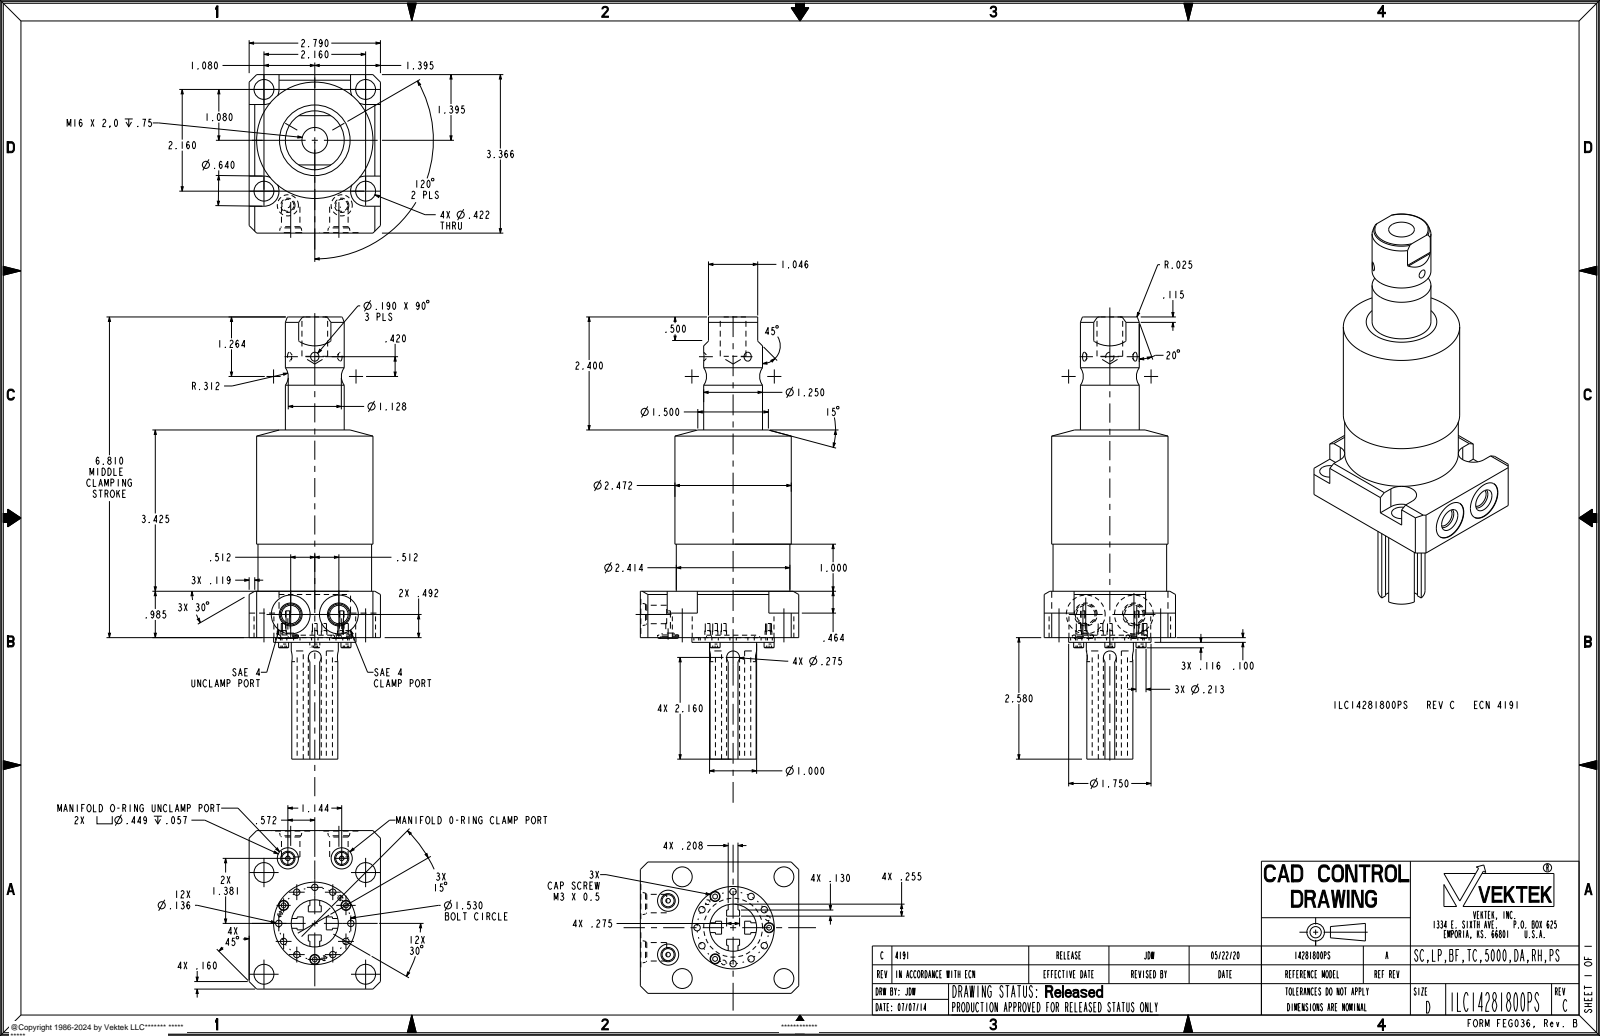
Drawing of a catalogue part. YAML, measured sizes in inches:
part_name: "ILC14281800PS"
step_written_by: "PRO/ENGINEER BY PARAMETRIC TECHNOLOGY CORPORATION, 2013320 (AUTOMOTIVE_DESIGN)"
units: inches
bodies: {solids: 1, faces: 283, planar: 133, cylindrical: 112, other: 38}
overall_size: [9.39, 3.366, 2.79]
volume: 28.24
surface_area: 88.39
round_holes:
  - {diameter: 0.136, count: 12}
  - {diameter: 0.1, count: 6}
  - {diameter: 0.422, count: 4}
  - {diameter: 0.098, count: 2}
  - {diameter: 0.256, count: 2}
  - {diameter: 0.392, count: 2}
  - {diameter: 0.449, count: 2}
  - {diameter: 0.825, count: 2}
  - {diameter: 0.546, count: 1}
  - {diameter: 1.13, count: 1}
round_bosses_or_shafts:
  - {diameter: 0.118, count: 6}
  - {diameter: 0.213, count: 3}
  - {diameter: 2.472, count: 1}
  - {diameter: 2.414, count: 1}
  - {diameter: 1.75, count: 1}
  - {diameter: 1.25, count: 1}
  - {diameter: 1, count: 1}
  - {diameter: 0.917, count: 1}
partial_cylinders:
  - {radius: 0.32, count: 4}
  - {radius: 0.03, count: 2}
  - {radius: 0.138, count: 2}
face_to_face_distances: [0.985, 2.79, 0.107, 0.382, 0.141, 0.349, 0.033, 0.241, 1.64, 1.15]
hole_center_spacings: [0.765, 1.325, 0.396, 0.765, 0.813, 1.082, 1.125, 1.478]
